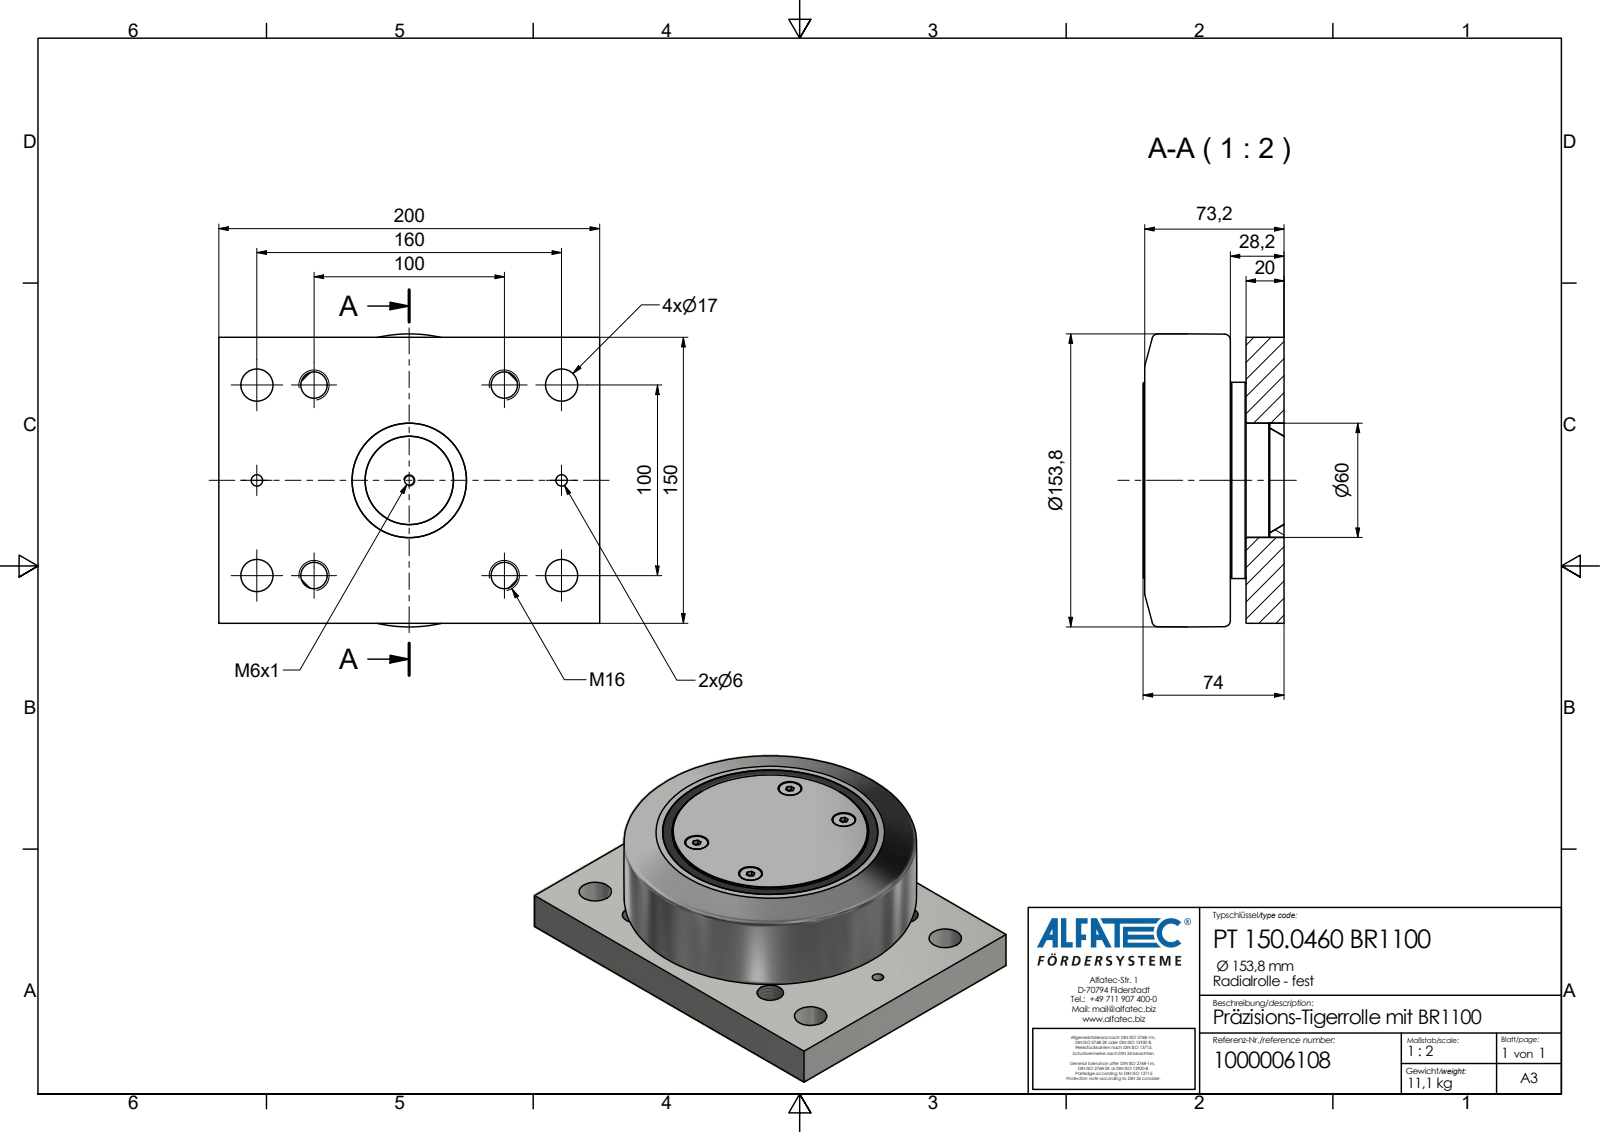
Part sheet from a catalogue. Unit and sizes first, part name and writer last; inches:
Units: inches
Overall size (bounding box): 7.874 × 6.055 × 2.913
Round holes (diameter × count): ⌀0.488 ×4, ⌀0.545 ×4, ⌀0.669 ×4, ⌀0.236 ×2
Round bosses / shafts (diameter × count): ⌀0.461 ×4, ⌀4.055 ×1, ⌀4.035 ×1, ⌀3.992 ×1
Main face-to-face distances: 0.787, 1.11, 0.323, 2.913, 2.126, 1.803, 5.906, 2.882, 2.094, 1.772
Hole centre spacings: 2.728, 3.937, 1.181, 1.327, 1.969, 2.296, 2.438, 2.822
Volume: 89.09 in³ · Surface area: 189.6 in²
Bodies: 1 solid, 78 faces (46 planar, 21 cylindrical, 11 other)
Part name (STEP PRODUCT): PT 150.0460 BR1100_Kontur
STEP written by: Autodesk Inventor 2020 (AP242_MANAGED_MODEL_BASED_3D_ENGINEERING_MIM_LF)
